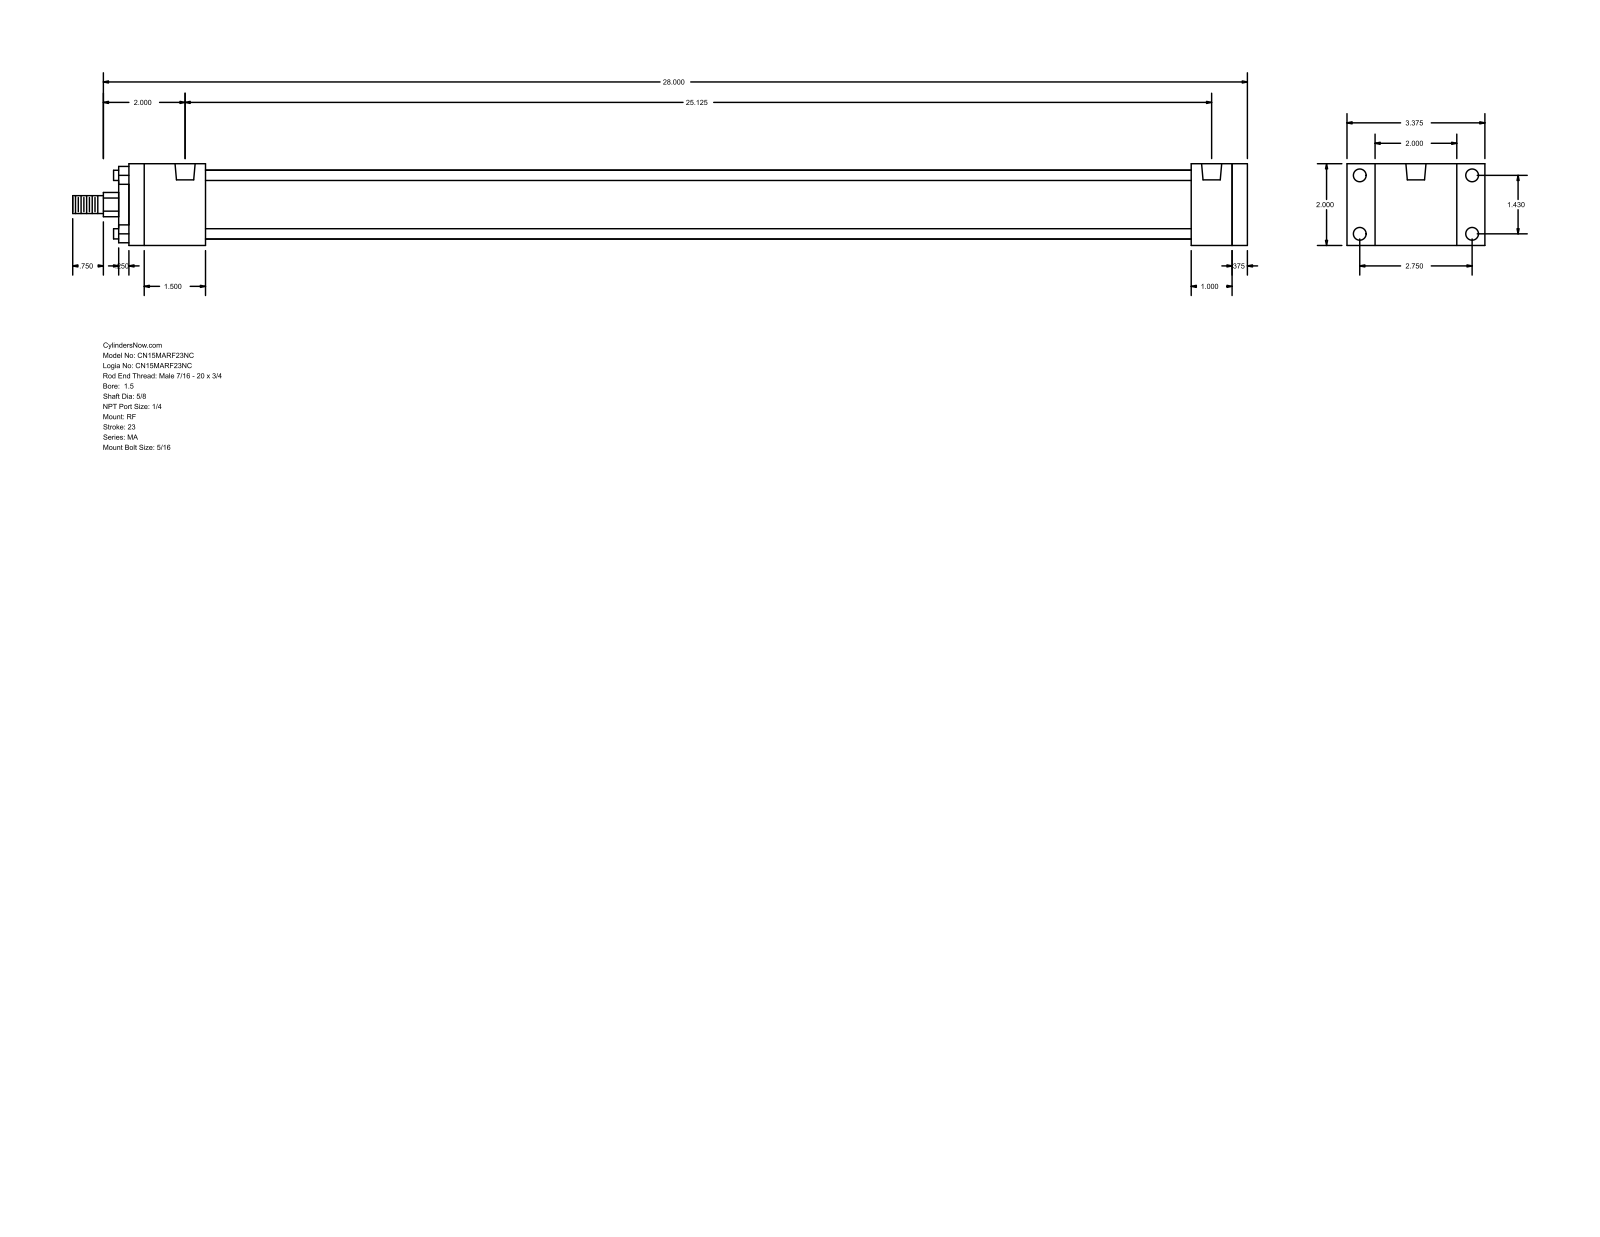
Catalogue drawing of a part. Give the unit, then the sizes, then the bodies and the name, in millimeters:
Units: millimetres
Overall size (bounding box): 730.25 × 85.72 × 50.8
Round holes (diameter × count): ⌀7.94 ×8, ⌀12.49 ×2
Round bosses / shafts (diameter × count): ⌀6.35 ×4, ⌀42.93 ×1, ⌀28.57 ×1, ⌀15.88 ×1, ⌀11.11 ×1
Partial cylindrical surfaces — rounded edges, fillets, slot ends (radius × count): R7.54 ×1
Main face-to-face distances: 50.8, 9.53, 695.32, 685.79, 25.4, 34.93, 660.39, 47.62, 612.77, 638.17
Hole centre spacings: 36.32, 69.84, 78.72, 638.18
Bodies: 0 solids, 92 faces (64 planar, 28 cylindrical, 0 other)
Part name (STEP PRODUCT): MA_RF__0150_0.625
STEP written by: GSSL Pune (CONFIG_CONTROL_DESIGN)
